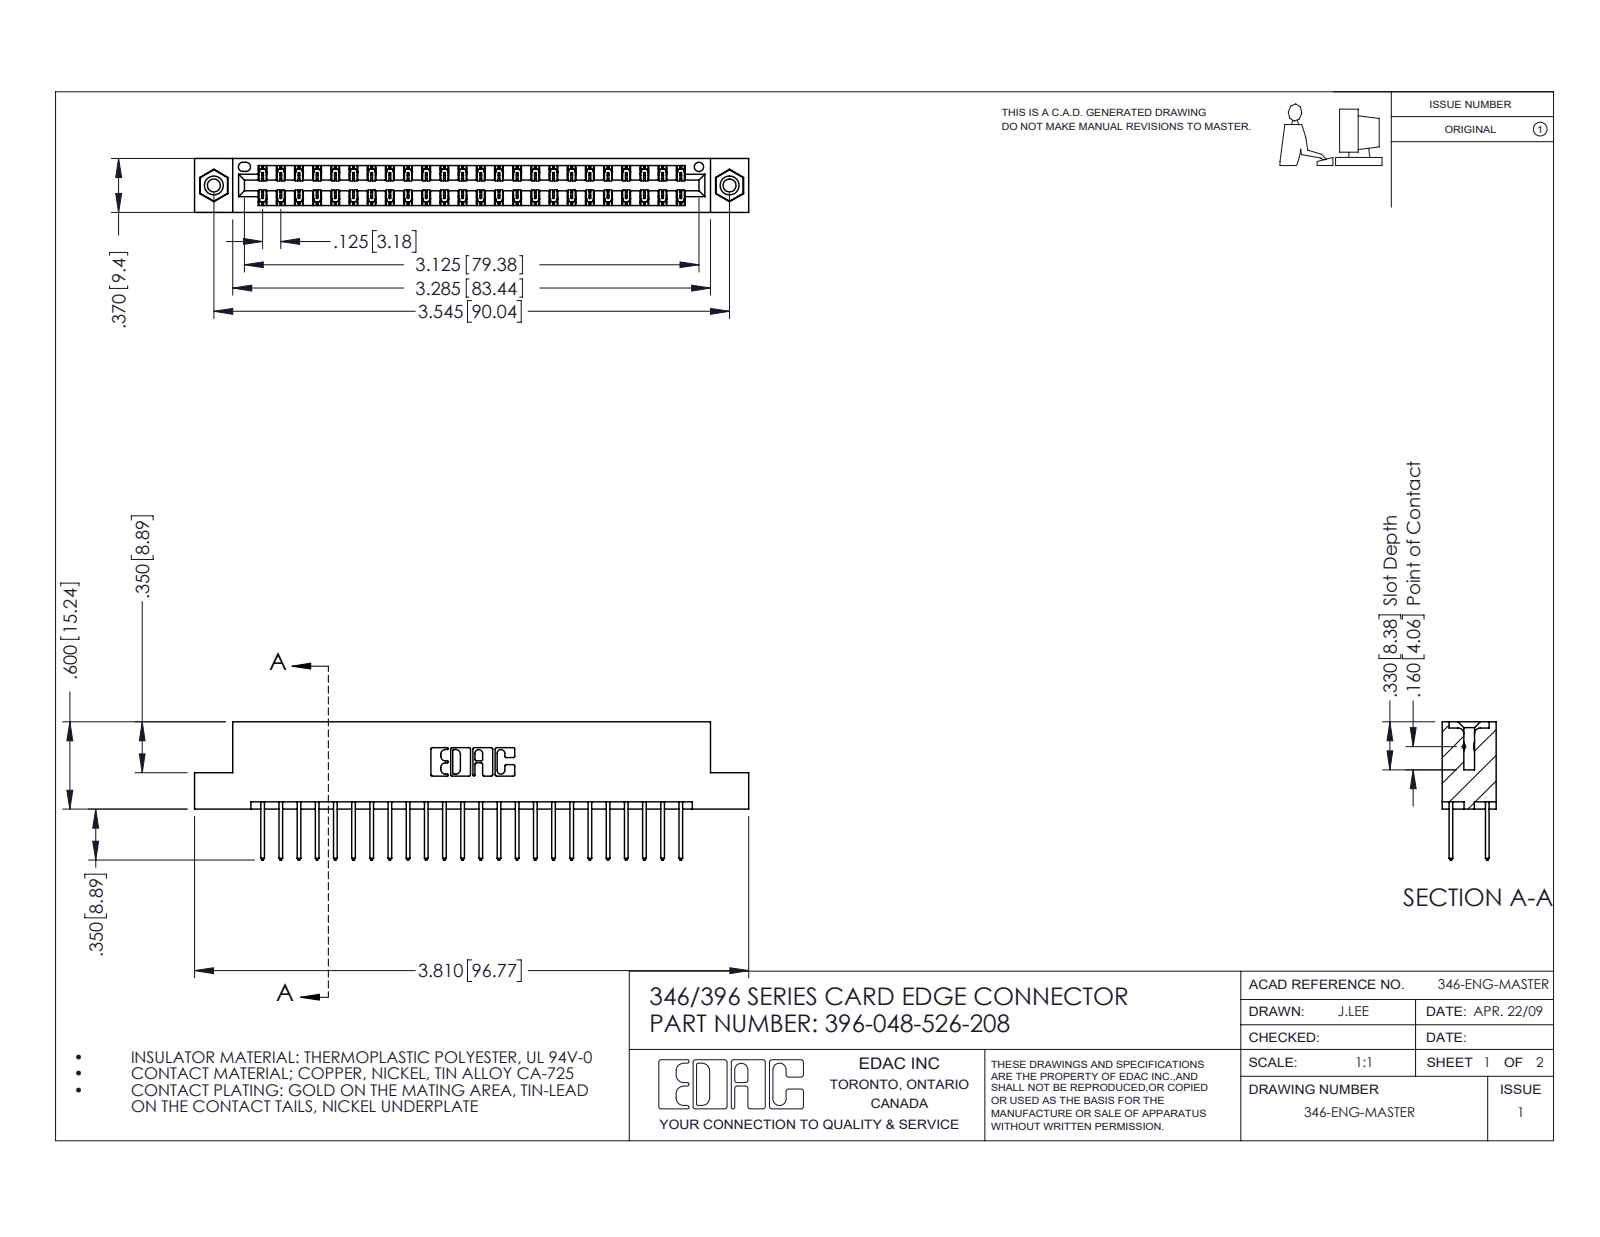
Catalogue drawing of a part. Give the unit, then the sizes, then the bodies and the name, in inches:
Units: inches
Overall size (bounding box): 3.81 × 0.95 × 0.37
Round holes (diameter × count): ⌀0.089 ×2, ⌀0.125 ×2, ⌀0.156 ×2, ⌀0.064 ×1
Round bosses / shafts (diameter × count): ⌀0.155 ×2
Partial cylindrical surfaces — rounded edges, fillets, slot ends (radius × count): R0.006 ×72, R0.01 ×48, R0.01 ×22, R0.007 ×6, R0.031 ×6, R0.026 ×3, R0.014 ×2, R0.022 ×2
Main face-to-face distances: 0.048, 0.322, 0.25, 0.37, 0.072, 0.298, 0.025, 0.275, 0.148, 0.222
Hole centre spacings: 0.246, 3.337, 3.545
Volume: 0.572 in³ · Surface area: 20.1 in²
Bodies: 51 solids, 2678 faces (1788 planar, 874 cylindrical, 16 other)
Part name (STEP PRODUCT): 345-292-001_345-293-126; 345-250-001_345-250-003-102; 346 Part_Flush Mounting Lugs - 0.156 Dia-TI; 396-048-526-208
STEP written by: SolidWorks 2016 (CONFIG_CONTROL_DESIGN)
